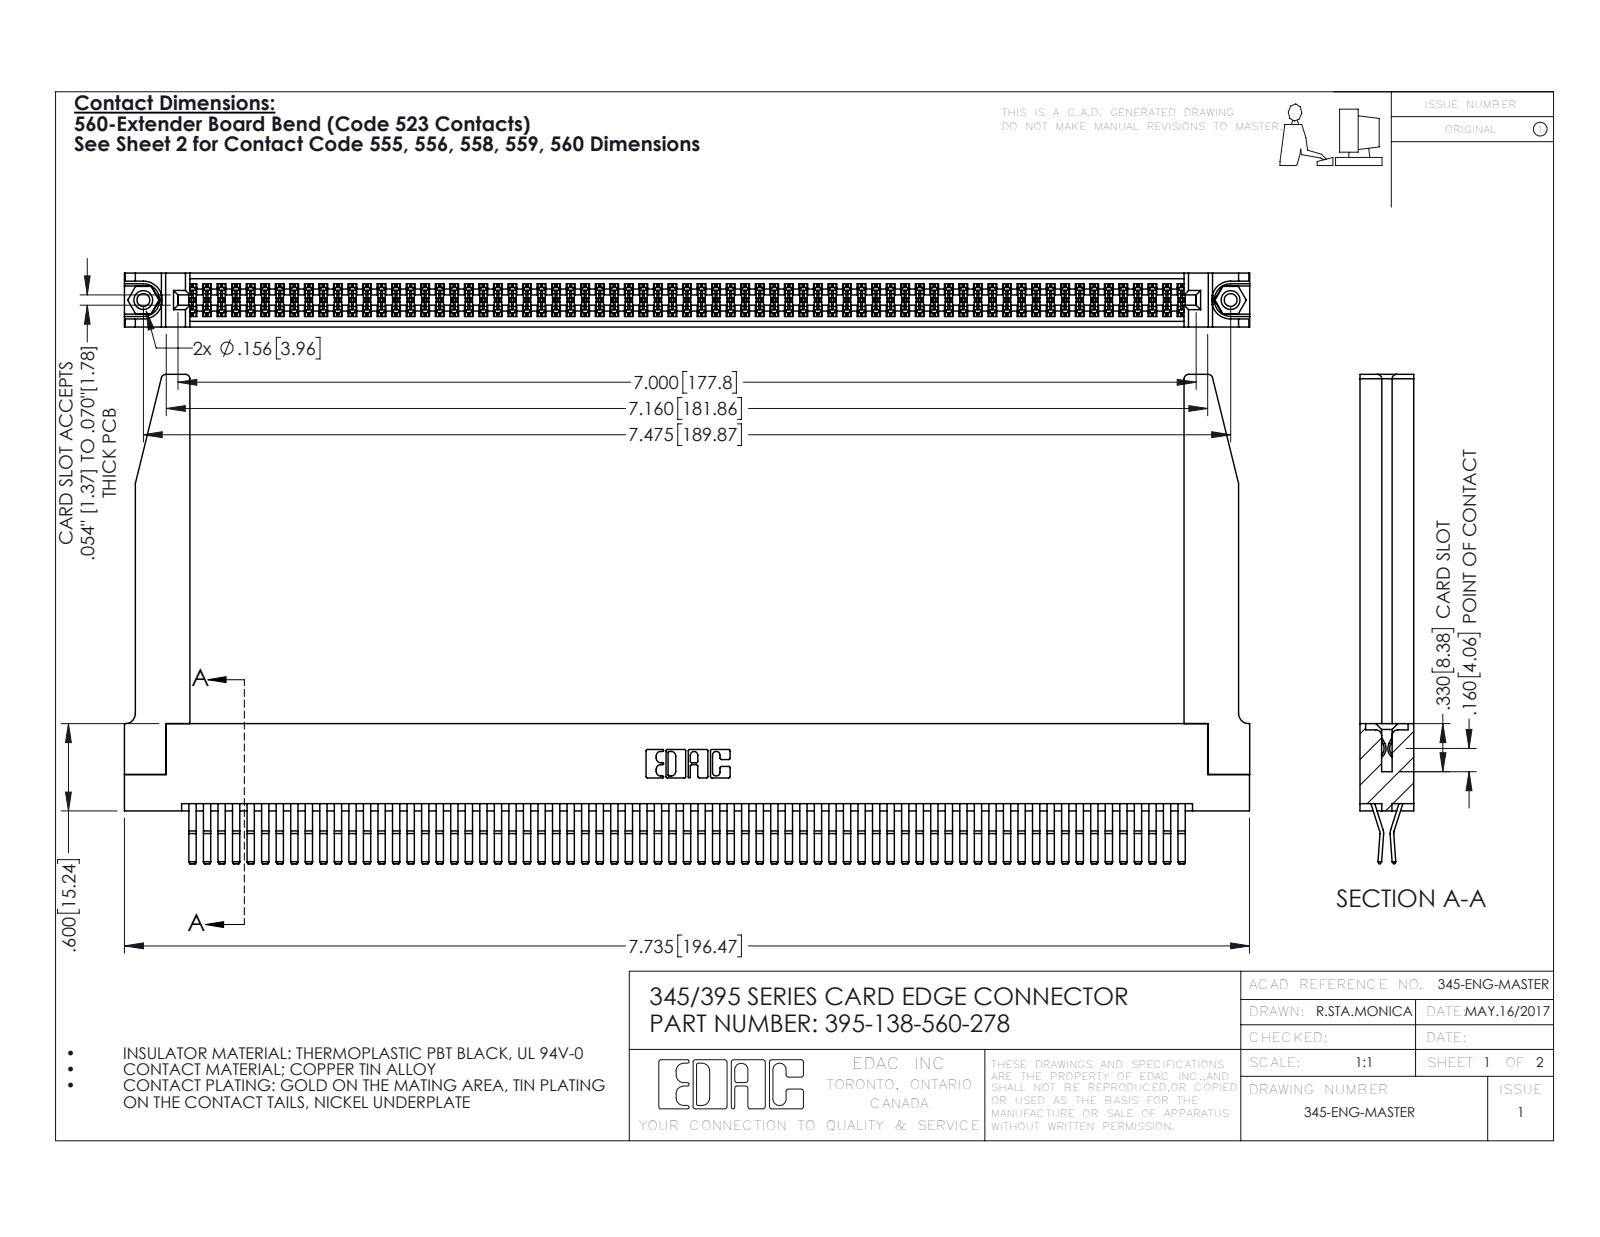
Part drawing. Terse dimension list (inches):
name: 345 Part_Flush Mounting Lugs - 0.156 Dia-TH; 345-292-001_560 Tail; 345-220-078_345-220-078; 395-138-560-278 (+1 more)
written by: SolidWorks 2016 (CONFIG_CONTROL_DESIGN)
unit: in
bodies: 143 solids, 7536 faces (4776 planar, 2708 cylindrical, 52 other)
size: 7.736 × 3.362 × 0.37
volume: 1.709 in³; area: 61.4 in²
holes: 2× ⌀0.089, 2× ⌀0.125, 2× ⌀0.156, 1× ⌀0.064
bosses: 2× ⌀0.155
rounds: 207× R0.006, 22× R0.01, 8× R0.03, 6× R0.007, 6× R0.031, 3× R0.026, 2× R0.01, 2× R0.014
face distances: 0.072, 0.025, 0.298, 0.37, 0.2, 0.098, 0.272, 0.225, 0.175, 0.149
hole spacings: 0.27, 7.239, 7.475
